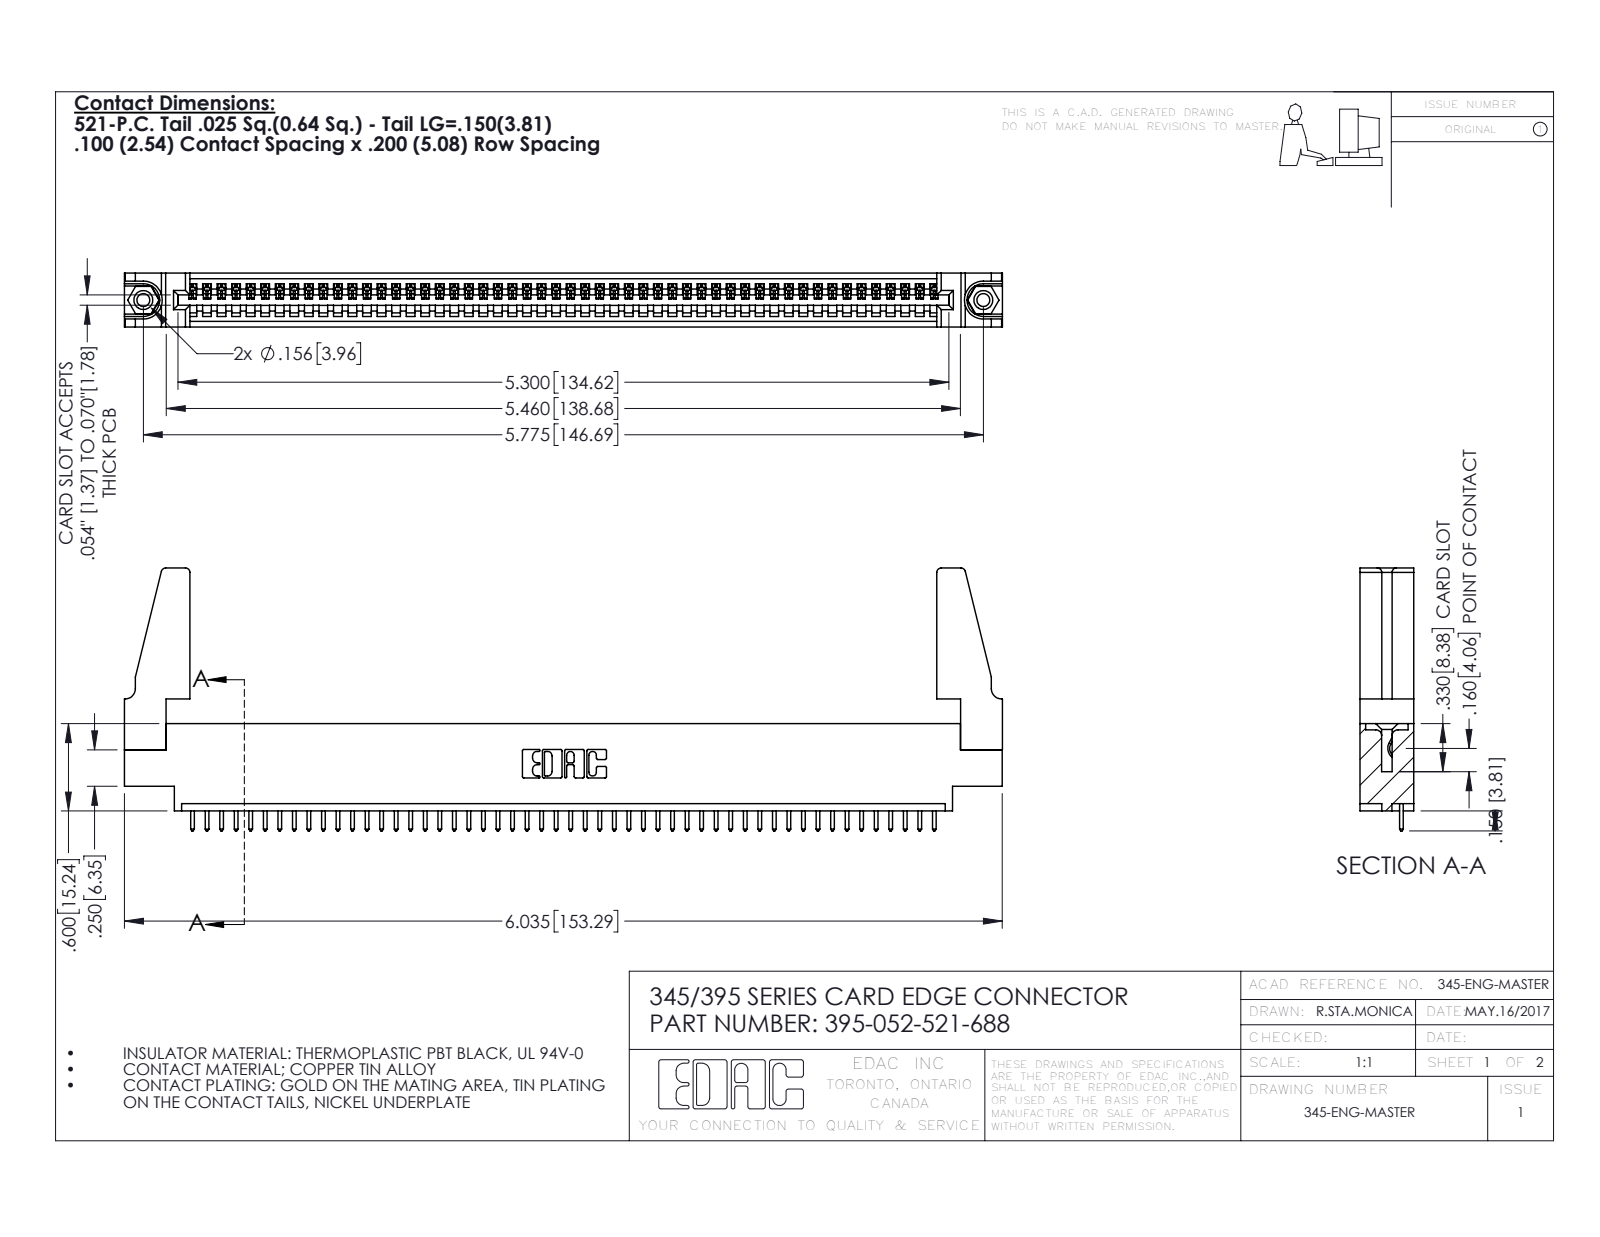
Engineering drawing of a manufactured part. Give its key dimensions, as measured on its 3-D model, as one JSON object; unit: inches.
{"part_name": "345-250-001_345-250-001-102; 345 Part_0.170 Offset - 0.156 Dia-TH; 345-292-001_345-293-121; 395-052-521-688 (+1 more)", "step_written_by": "SolidWorks 2016 (CONFIG_CONTROL_DESIGN)", "units": "inches", "bodies": {"solids": 57, "faces": 3270, "planar": 2236, "cylindrical": 1018, "other": 16}, "overall_size": [6.036, 1.807, 0.37], "volume_in3": 1.076, "surface_area_in2": 33.99, "round_holes": [[0.089, 2], [0.125, 2], [0.156, 2], [0.064, 1]], "round_bosses_or_shafts": [[0.155, 2]], "partial_cylinders_radius": [[0.006, 104], [0.01, 104], [0.01, 22], [0.03, 8], [0.007, 6], [0.031, 6], [0.026, 3], [0.031, 2]], "face_to_face_distances": [0.072, 0.298, 0.37, 0.098, 0.272, 0.025, 0.2, 0.225, 0.175, 0.149], "hole_center_spacings": [0.27, 5.539, 5.775]}
